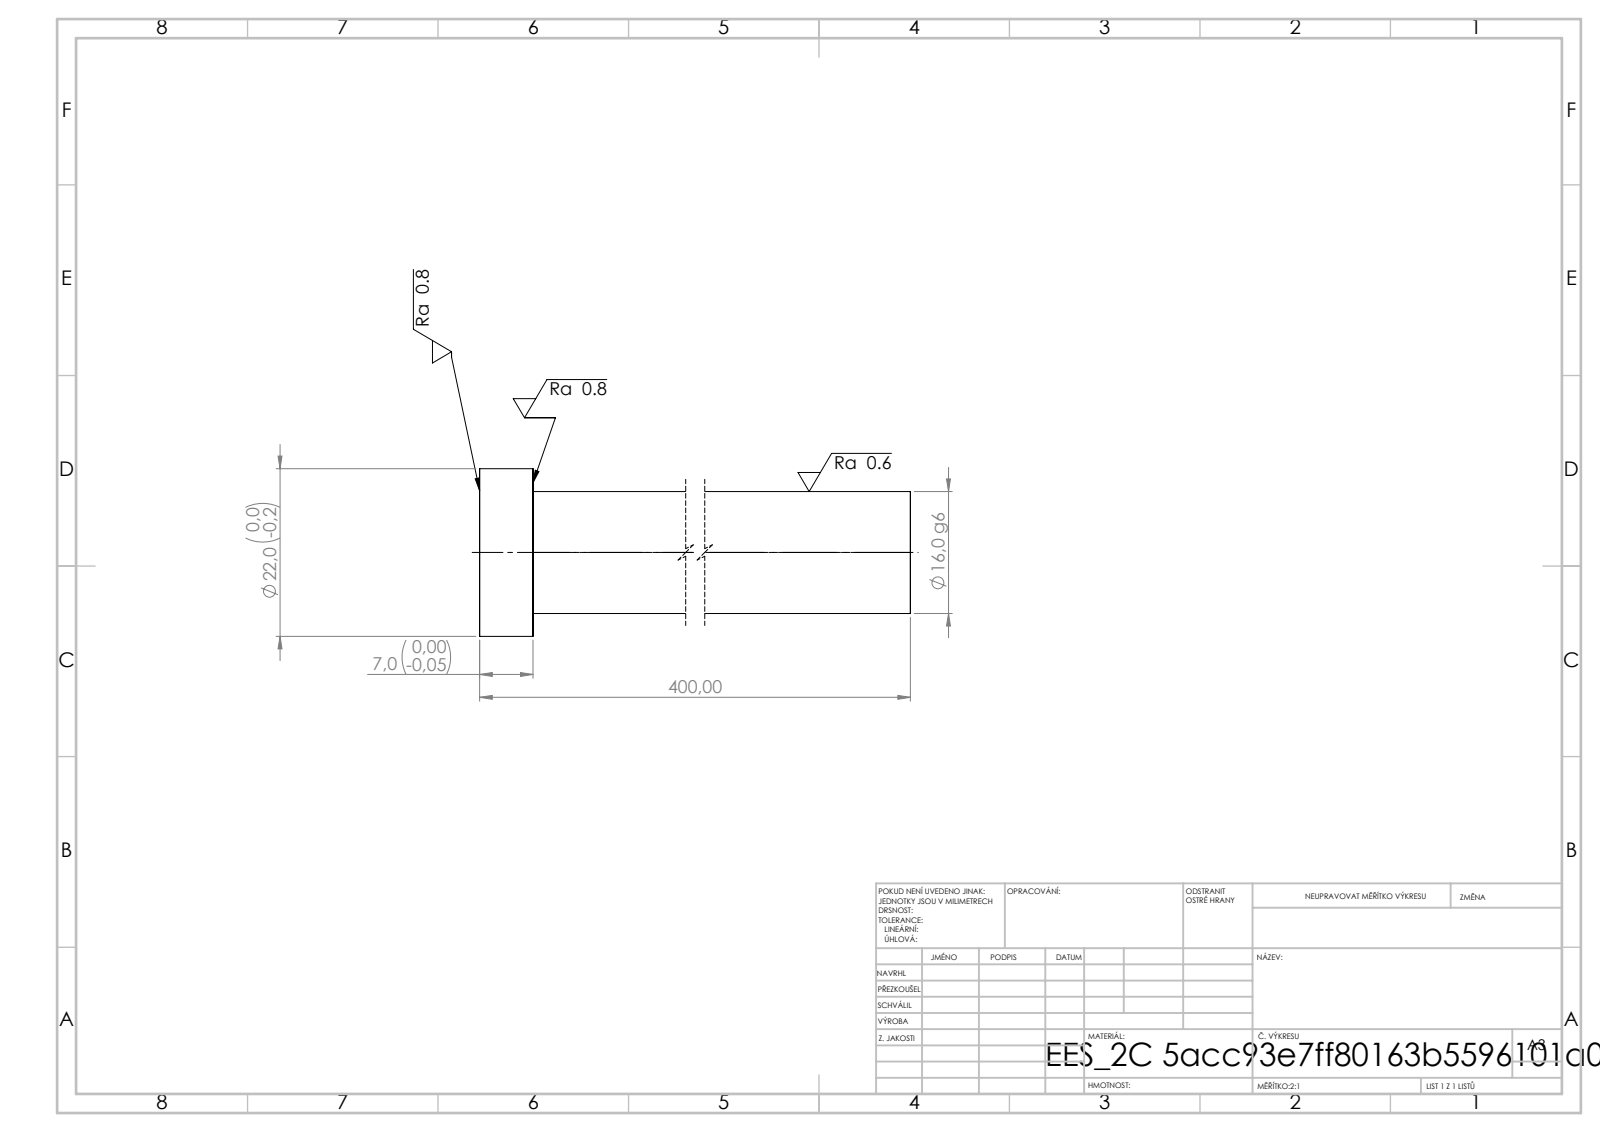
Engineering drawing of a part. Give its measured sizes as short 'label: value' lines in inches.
written by: SolidWorks 2019 (CONFIG_CONTROL_DESIGN)
unit: in
bodies: 1 solid, 7 faces (3 planar, 4 cylindrical, 0 other)
size: 15.748 × 0.866 × 0.866
volume: 4.984 in³; area: 32.55 in²
bosses: 1× ⌀0.866, 1× ⌀0.63
face distances: 15.748, 0.276, 15.472
